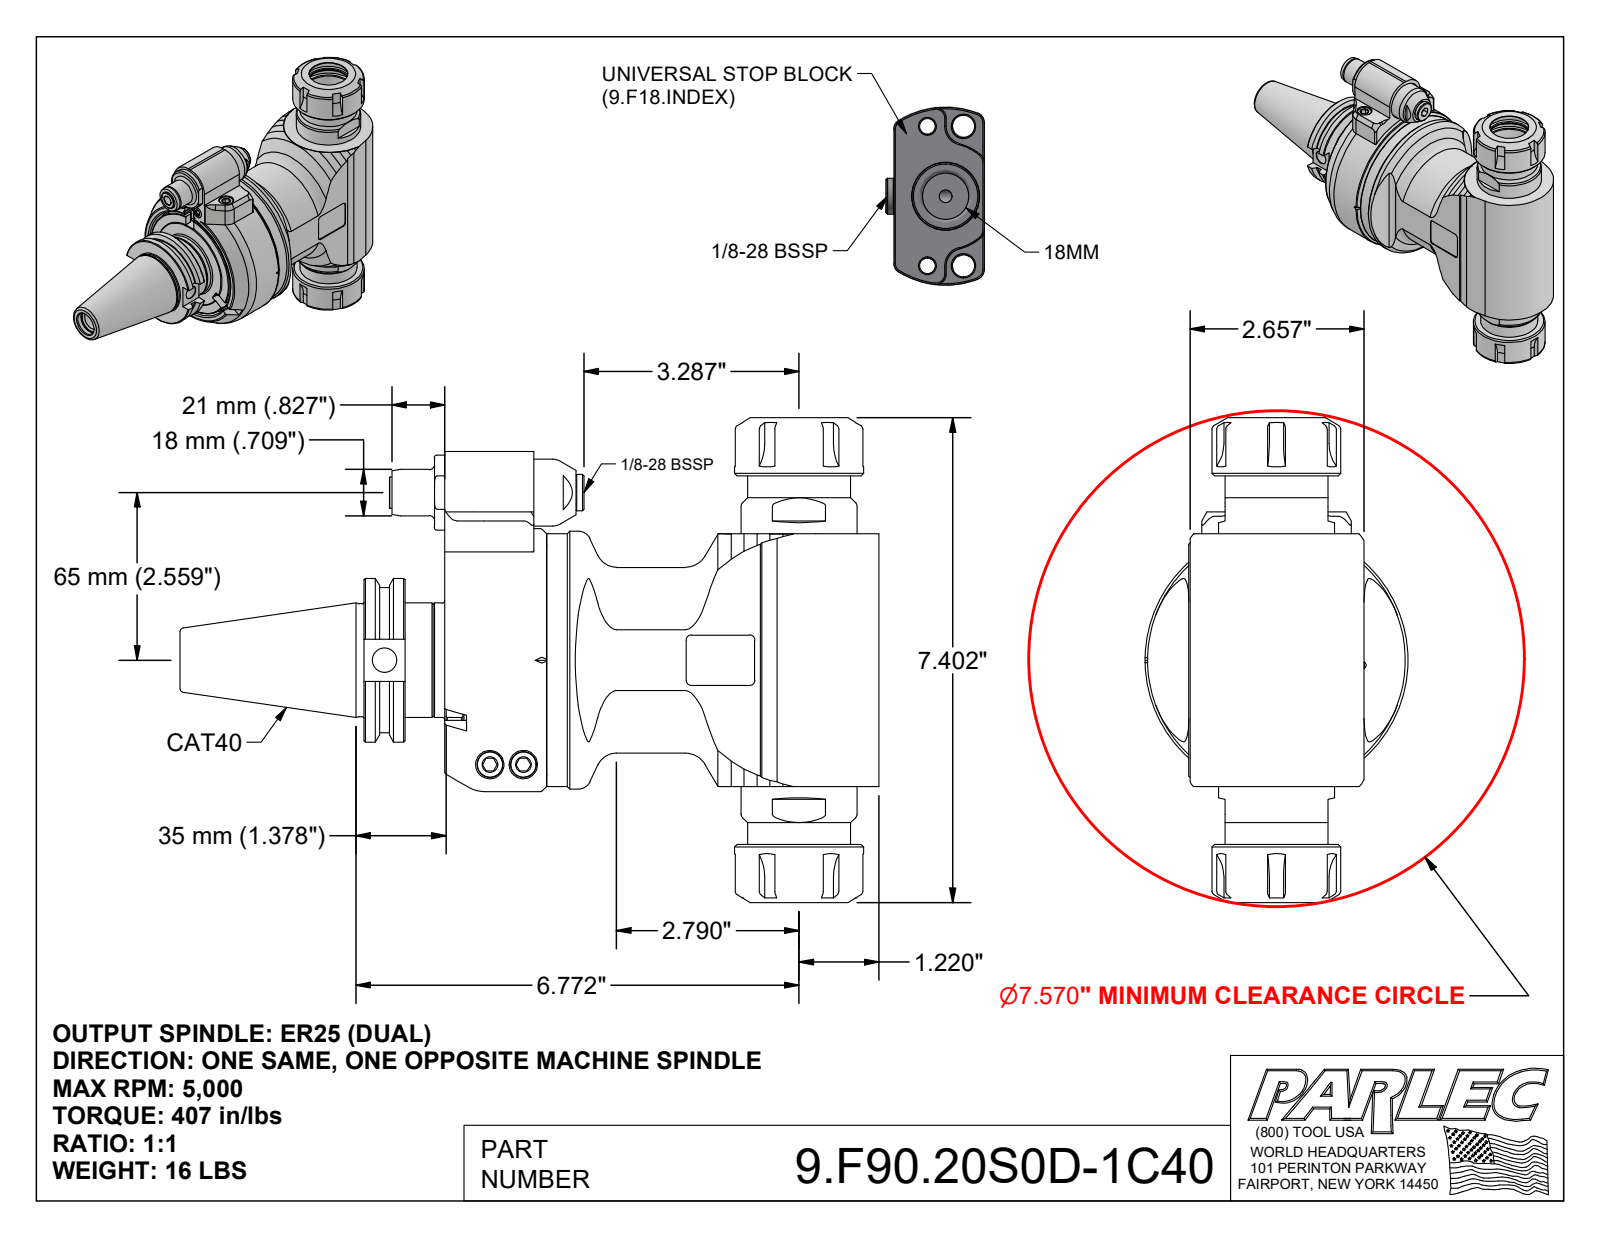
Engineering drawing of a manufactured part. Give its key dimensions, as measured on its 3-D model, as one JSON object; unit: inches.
{"part_name": "9.F90.20S0D-1C40", "step_written_by": "Autodesk Inventor 2022 (AUTOMOTIVE_DESIGN)", "units": "inches", "bodies": {"solids": 1, "faces": 669, "planar": 287, "cylindrical": 170, "other": 212}, "overall_size": [10.679, 7.402, 4.016], "volume_in3": 74.63, "surface_area_in2": 228.6, "round_holes": [[0.165, 4], [0.256, 3], [0.102, 2], [0.13, 2], [0.315, 2], [0.409, 2], [0.433, 2], [0.492, 2], [1.063, 2], [0.098, 1], [0.118, 1], [0.276, 1]], "round_bosses_or_shafts": [[0.394, 4], [0.472, 3], [1.575, 2], [0.709, 2], [0.236, 2], [0.098, 2], [4.016, 1], [3.937, 1]], "partial_cylinders_radius": [[0.039, 14], [0.079, 12], [0.591, 12], [0.118, 6], [0.157, 4], [0.02, 2], [0.315, 2], [0.551, 2]], "face_to_face_distances": [0.02, 0.335, 1.28, 0.276, 0.886, 1.26, 2.677, 0.256, 0.059, 0.197], "hole_center_spacings": [0.276, 0.504, 0.74, 0.996, 1.916, 0.512, 0.551, 0.63]}
